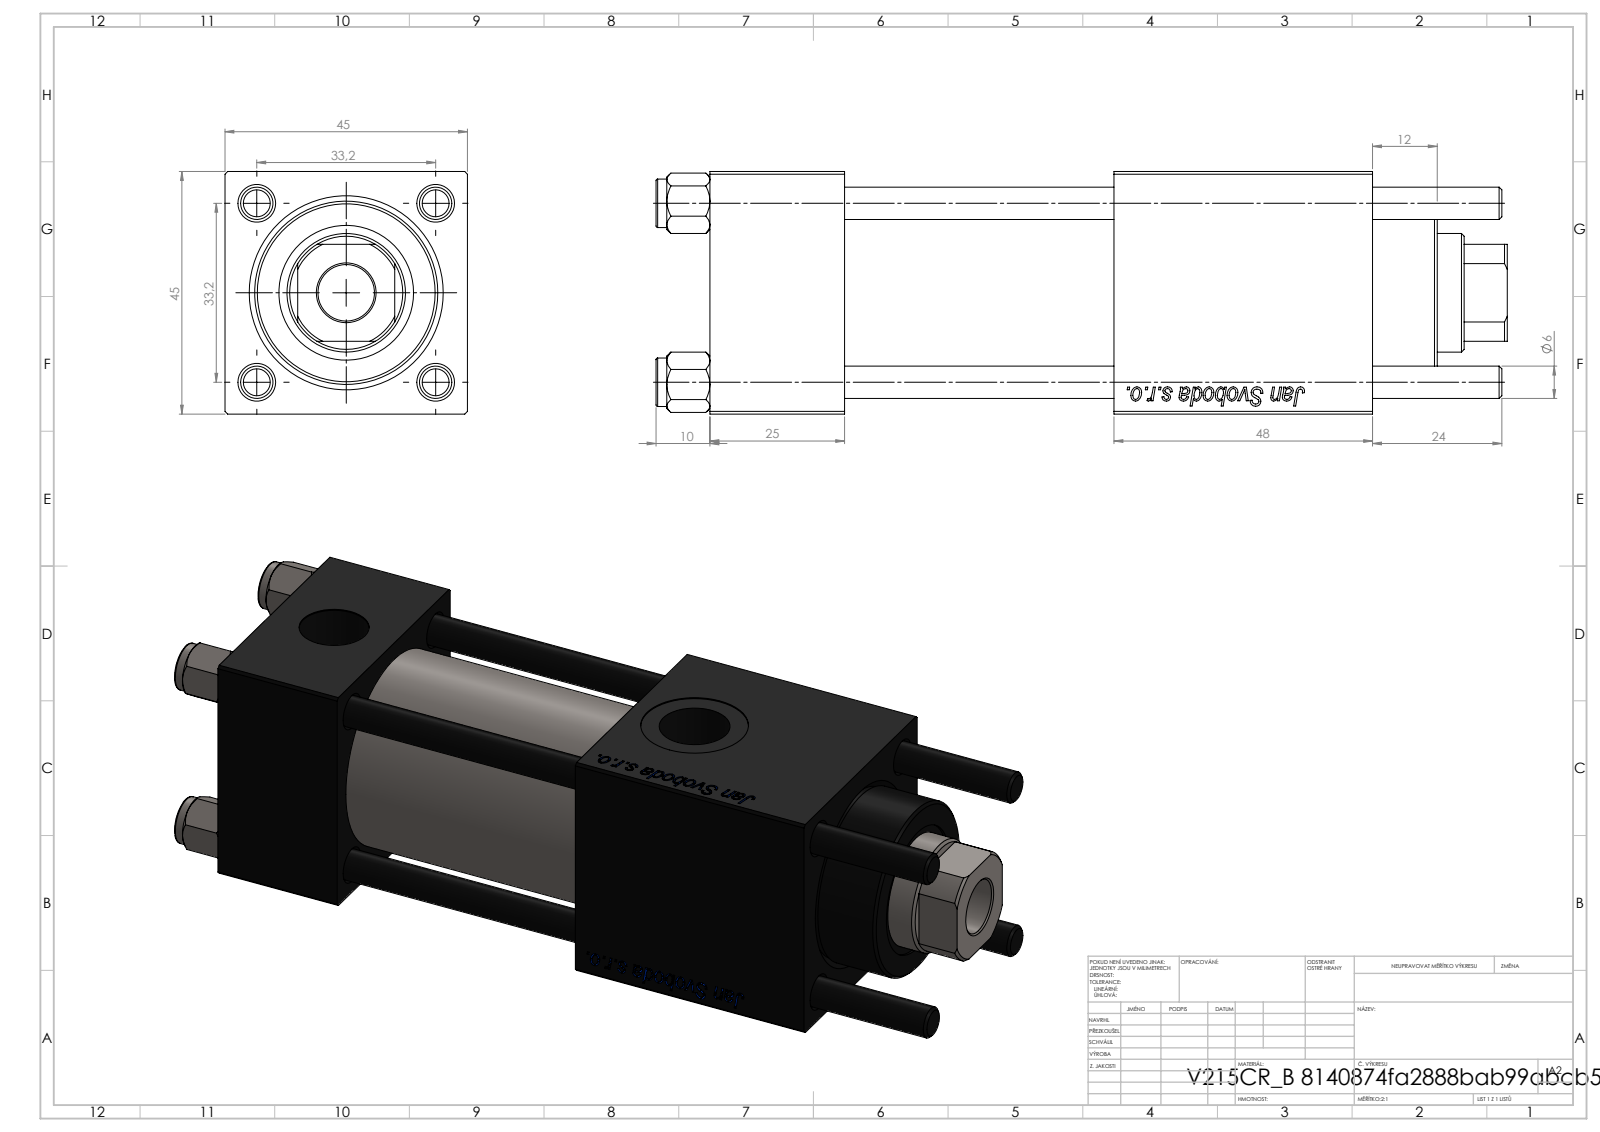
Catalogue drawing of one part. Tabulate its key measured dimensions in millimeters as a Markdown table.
| quantity | value |
| --- | --- |
| part name | V215CR_VCP_B; V215CR_B-1; V215_VC_A; NUT_M5_B (+1 more) |
| STEP written by | SolidWorks 2019 (CONFIG_CONTROL_DESIGN) |
| units | millimeters |
| bodies | 11 solids, 1156 faces (429 planar, 79 cylindrical, 648 other) |
| overall size | 158 × 45 × 45 |
| volume | 214 289 mm³ |
| surface area | 76 775 mm² |
| round holes (diameter × count) | 6 × 4, 7 × 2, 13.16 × 2, 10.5 × 1, 13 × 1, 20 × 1, 22 × 1, 24 × 1, 25 × 1, 32 × 1, 33 × 1 |
| round bosses / shafts (diameter × count) | 9 × 4, 38 × 1, 34 × 1 |
| partial cylindrical surfaces (radius × count) | 10.5 × 1 |
| main face-to-face distances | 45, 25, 50, 123, 75, 98, 48, 94.3, 69.3, 19.3 |
| hole center spacings | 23.48, 33.2, 46.95, 75.66 |
